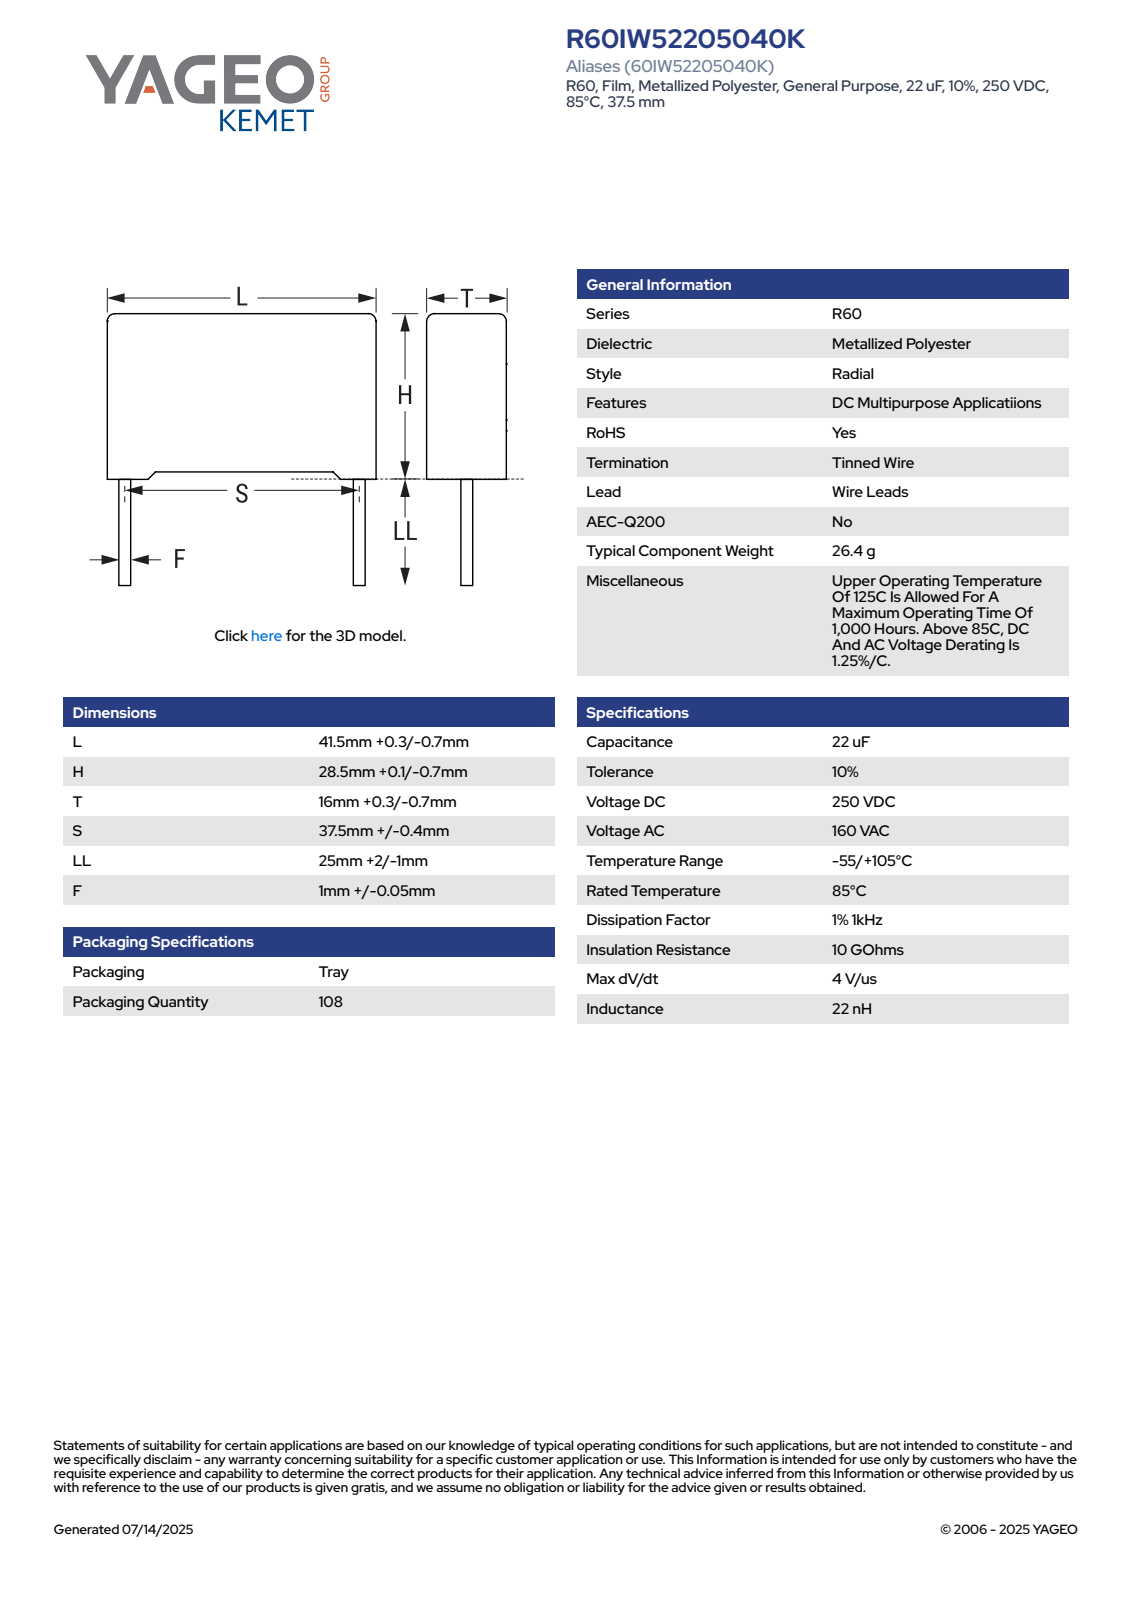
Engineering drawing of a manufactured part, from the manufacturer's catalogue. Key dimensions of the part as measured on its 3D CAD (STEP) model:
Part name (STEP PRODUCT): CFR_RB2_41.5X28.5X16_L41.8H28.6T16.3S37.5LL27F1.05
STEP written by: SolidWorks 2021 (AUTOMOTIVE_DESIGN)
Units: millimetres
Bodies: 4 solids, 85 faces (77 planar, 8 cylindrical, 0 other)
Overall size (bounding box): 55.6 × 41.8 × 16.3
Volume: 18 938 mm³ · Surface area: 4 942 mm²
Round bosses / shafts (diameter × count): ⌀1.05 ×2
Partial cylindrical surfaces — rounded edges, fillets, slot ends (radius × count): R0.5 ×4
Main face-to-face distances: 16.3, 27.61, 41.8, 27.85, 0.75, 0.99, 28.6, 16.31, 1.39, 40.41
